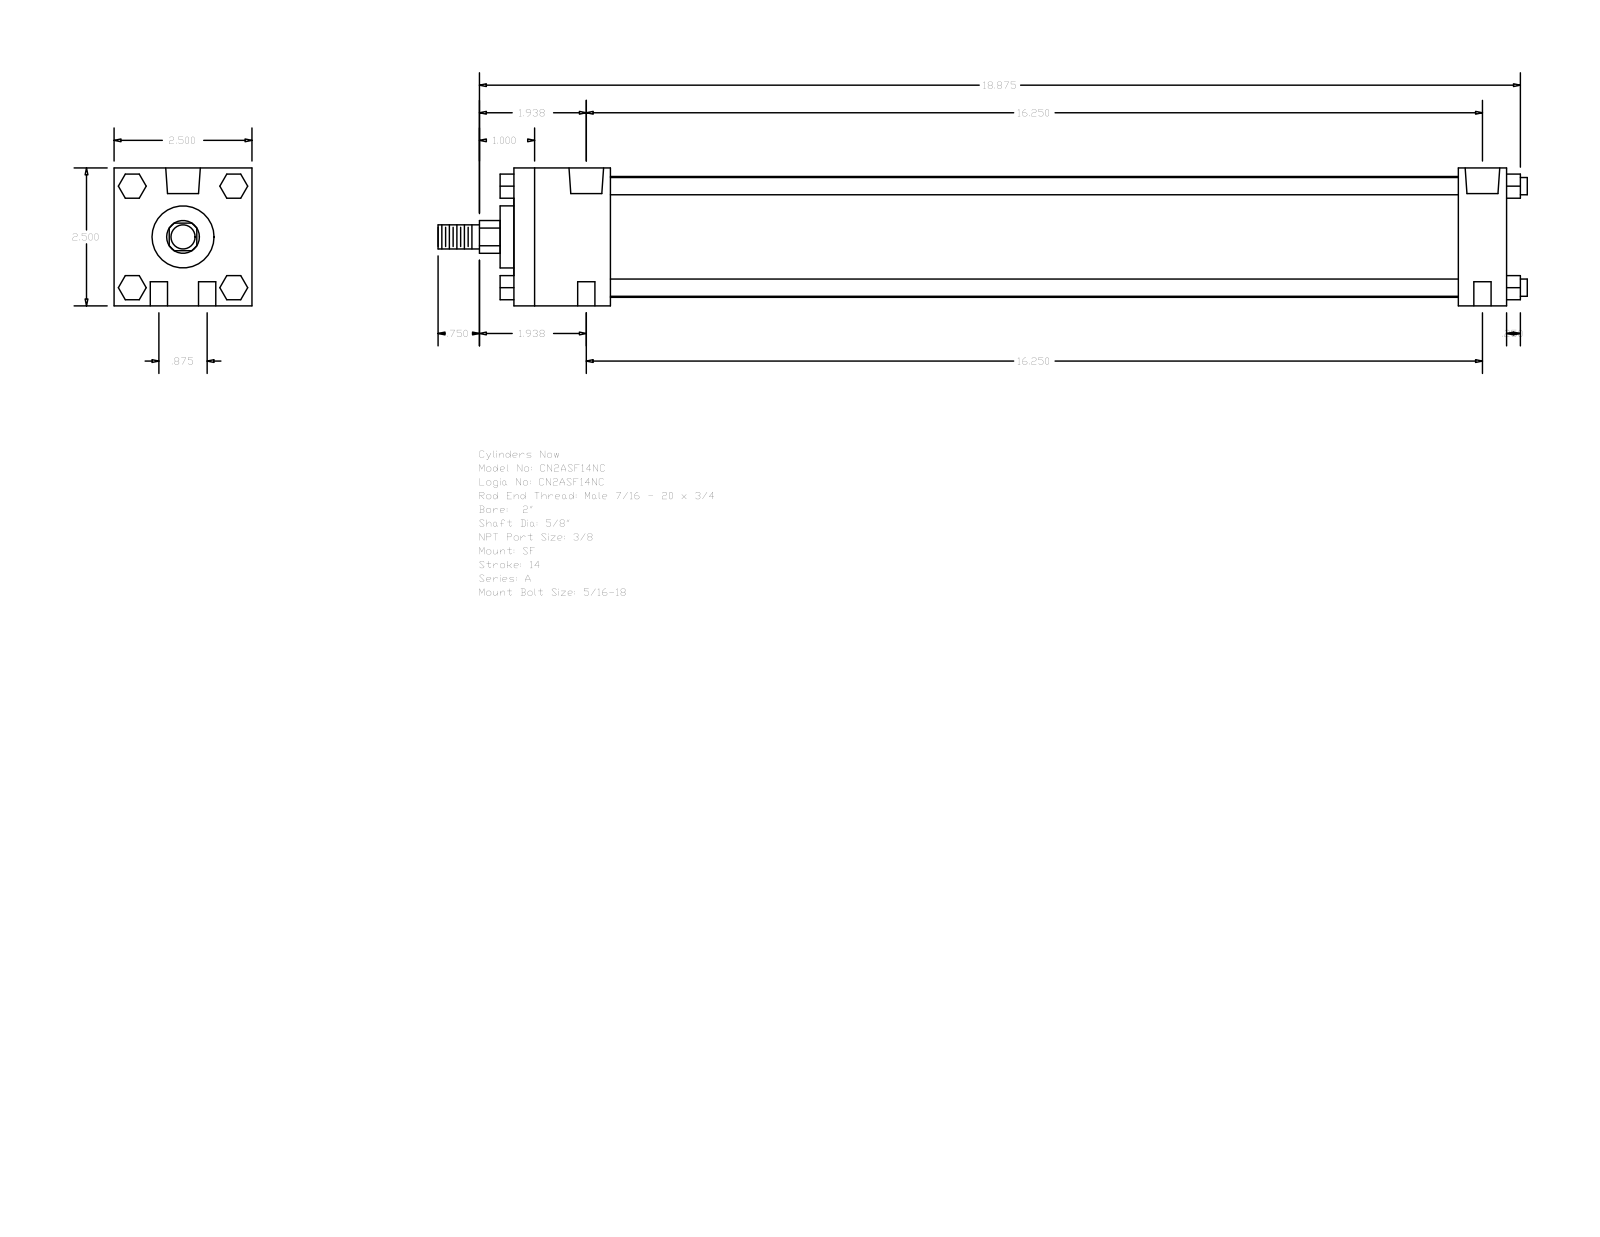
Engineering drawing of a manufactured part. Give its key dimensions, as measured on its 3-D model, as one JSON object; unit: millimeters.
{"part_name": "A_SF__0200_0.625", "step_written_by": "GSSL Pune (CONFIG_CONTROL_DESIGN)", "units": "millimeters", "bodies": {"solids": 0, "faces": 124, "planar": 94, "cylindrical": 30, "other": 0}, "overall_size": [501.65, 63.5, 63.5], "round_holes": [[7.94, 4], [5.56, 2], [15.93, 2]], "round_bosses_or_shafts": [[7.94, 4], [55.63, 1], [28.57, 1], [15.88, 1], [11.11, 1]], "partial_cylinders_radius": [[7.54, 1]], "face_to_face_distances": [63.5, 457.19, 434.97, 22.22, 44.45, 390.52, 412.74, 50.8, 6.35, 441.32], "hole_center_spacings": [11.11, 412.9, 412.75, 22.22, 413.35, 404.8]}
